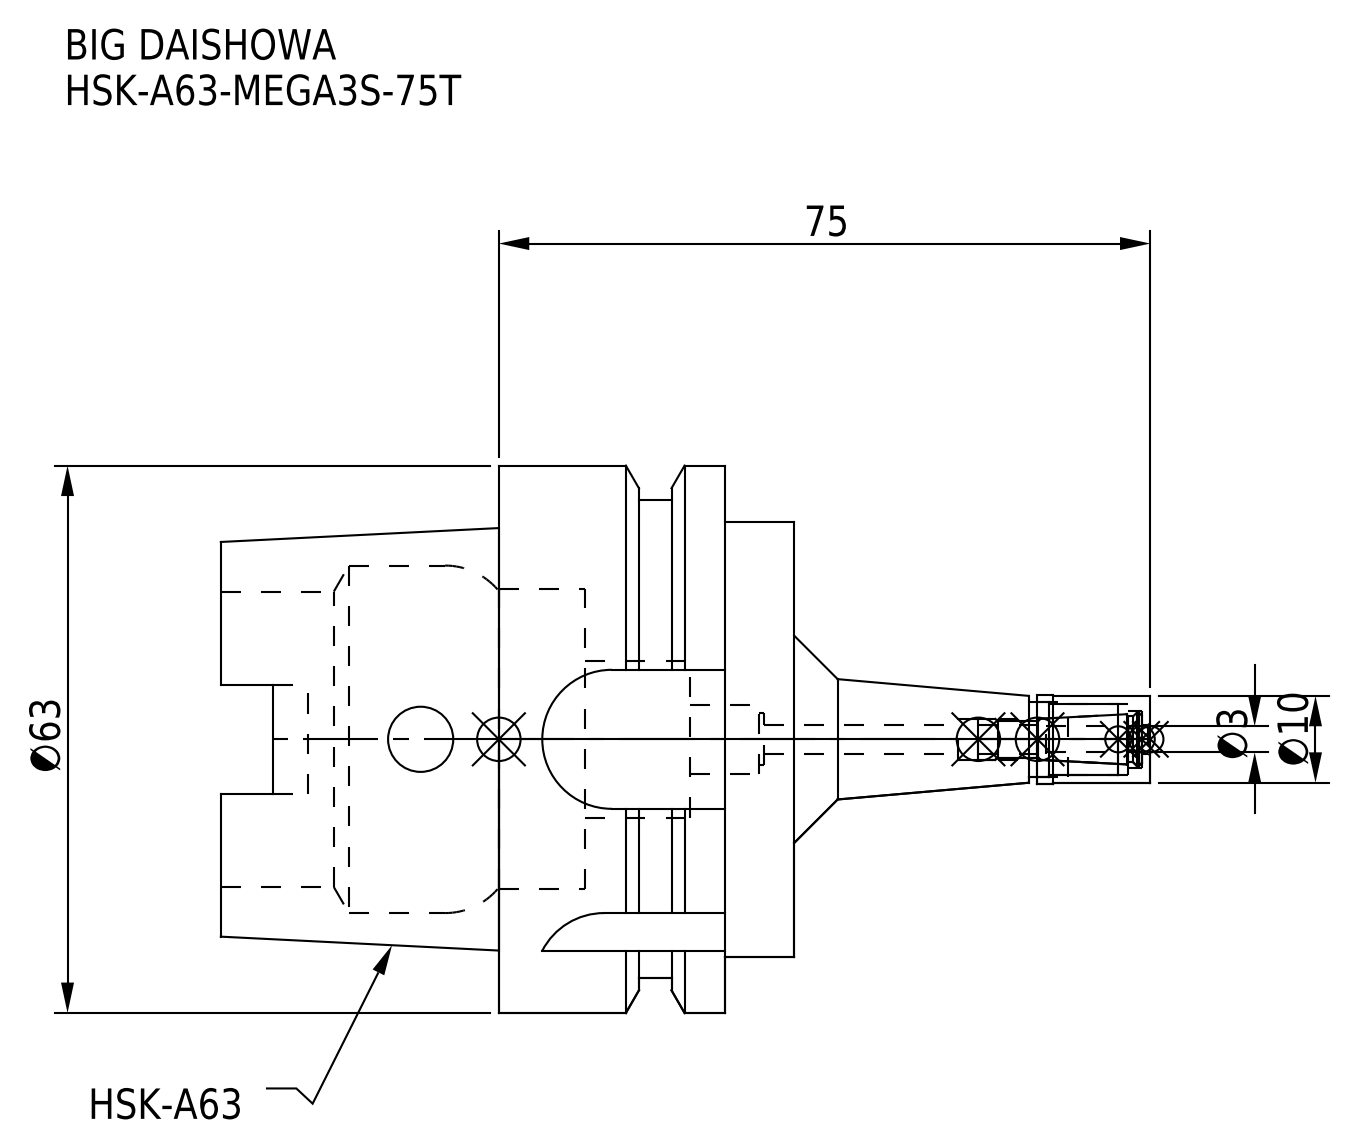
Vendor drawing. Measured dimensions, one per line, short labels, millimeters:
name: HA63MS03075T-030_ASM.stp; HSK-A63-MEGA3S-75T-030-FreeParts; HSK-A63-MEGA3S-75T_1.stp; HSK-A63-MEGA3S-75T (+3 more)
written by: SolidWorks 2019 (CONFIG_CONTROL_DESIGN)
unit: mm
bodies: 2 solids, 125 faces (48 planar, 55 cylindrical, 22 other)
size: 107 × 63 × 63
volume: 101 430 mm³; area: 26 310 mm²
holes: 1× ⌀3.3, 1× ⌀3.4, 1× ⌀4.7, 1× ⌀6, 1× ⌀6.6, 1× ⌀7.5, 1× ⌀8, 1× ⌀8.2, 1× ⌀8.7, 1× ⌀18, 1× ⌀34, 1× ⌀34.5
bosses: 1× ⌀63, 1× ⌀55, 1× ⌀50, 1× ⌀10.3, 1× ⌀10
rounds: 4× R2.88, 4× R8
face distances: 34, 26, 8, 24.05, 16.05, 9.95, 32, 66, 58, 41.95
